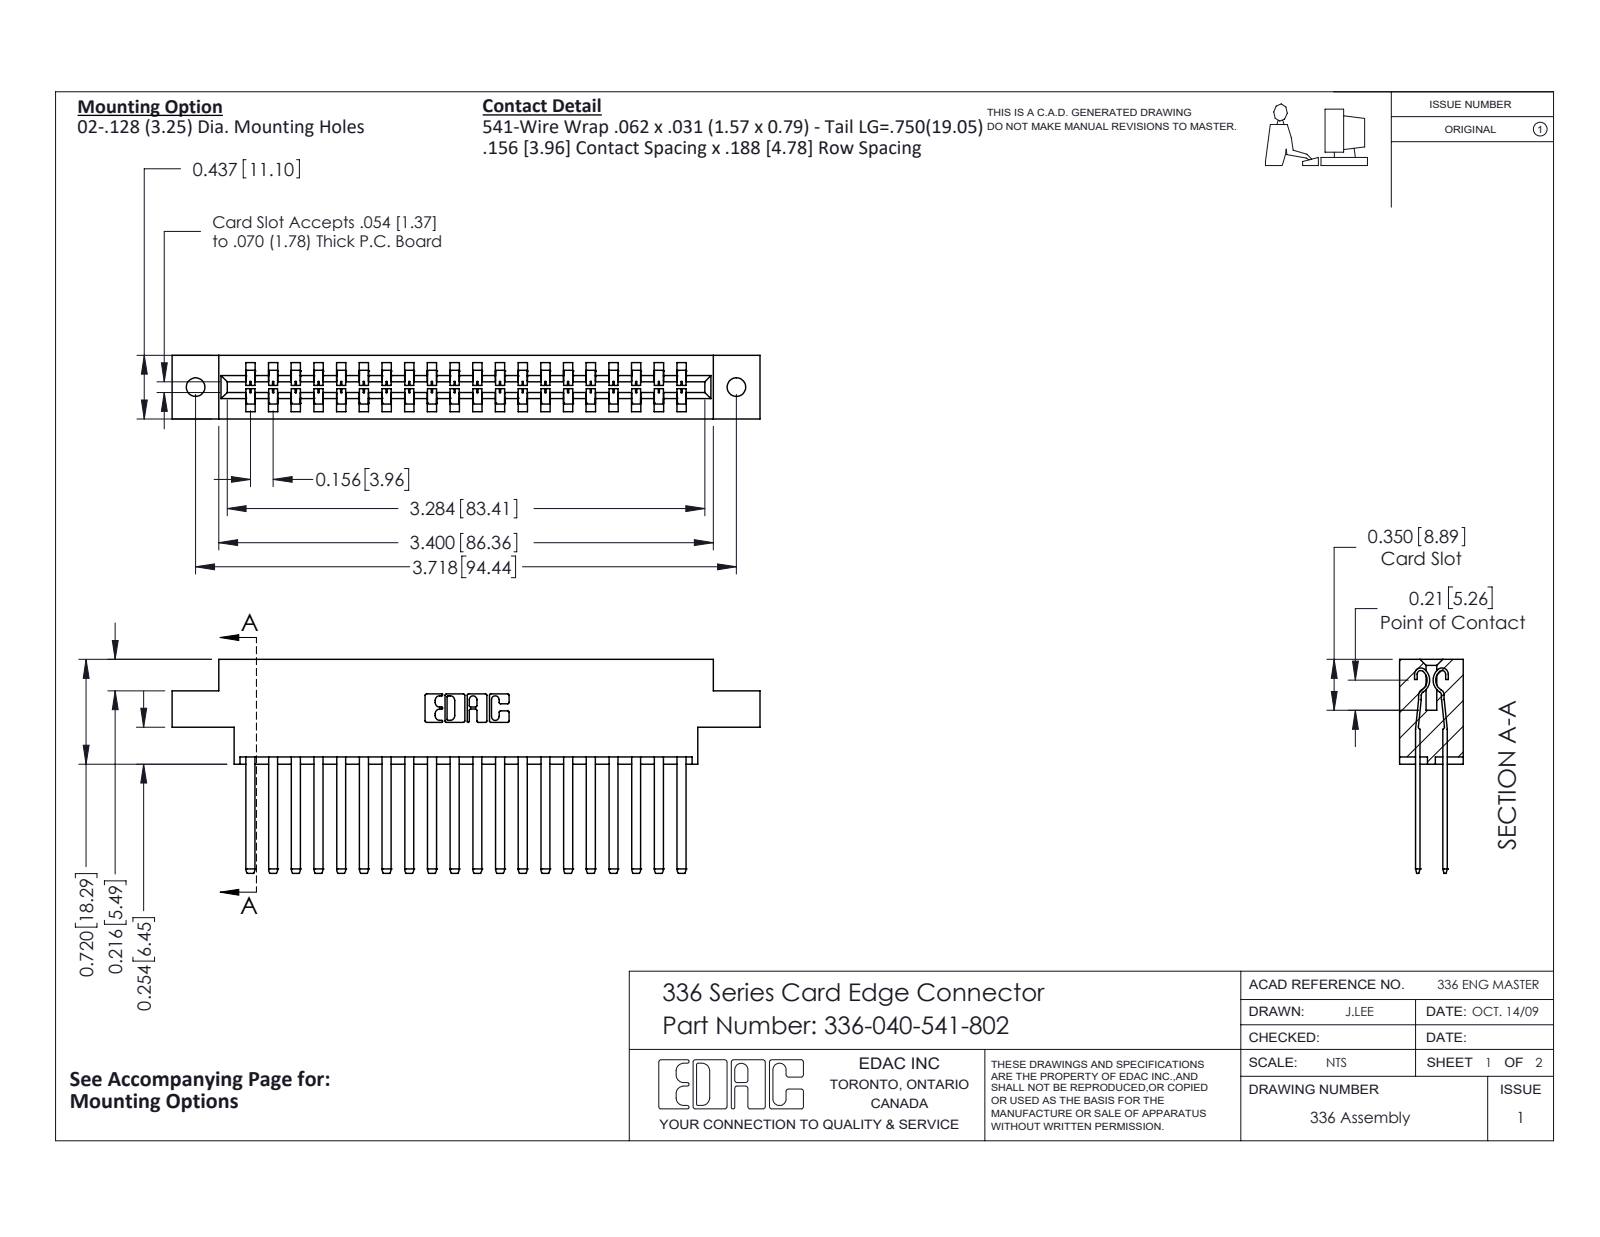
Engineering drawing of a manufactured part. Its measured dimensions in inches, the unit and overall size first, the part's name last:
Units: inches
Overall size (bounding box): 4.041 × 1.47 × 0.437
Round holes (diameter × count): ⌀0.128 ×2
Partial cylindrical surfaces — rounded edges, fillets, slot ends (radius × count): R0.004 ×80, R0.056 ×40, R0.01 ×22, R0.007 ×6, R0.031 ×6, R0.022 ×4, R0.04 ×4, R0.026 ×3
Main face-to-face distances: 0.188, 0.328, 0.14, 0.297, 0.109, 0.031, 0.437, 0.033, 0.156, 0.181
Hole centre spacings: 3.718
Volume: 0.912 in³ · Surface area: 28.84 in²
Bodies: 41 solids, 1798 faces (1114 planar, 684 cylindrical, 0 other)
Part name (STEP PRODUCT): 336-290-001_336-290-541; 336 Part_Offset - .128 Dia; 336-040-541-802
STEP written by: SolidWorks 2020 (CONFIG_CONTROL_DESIGN)
